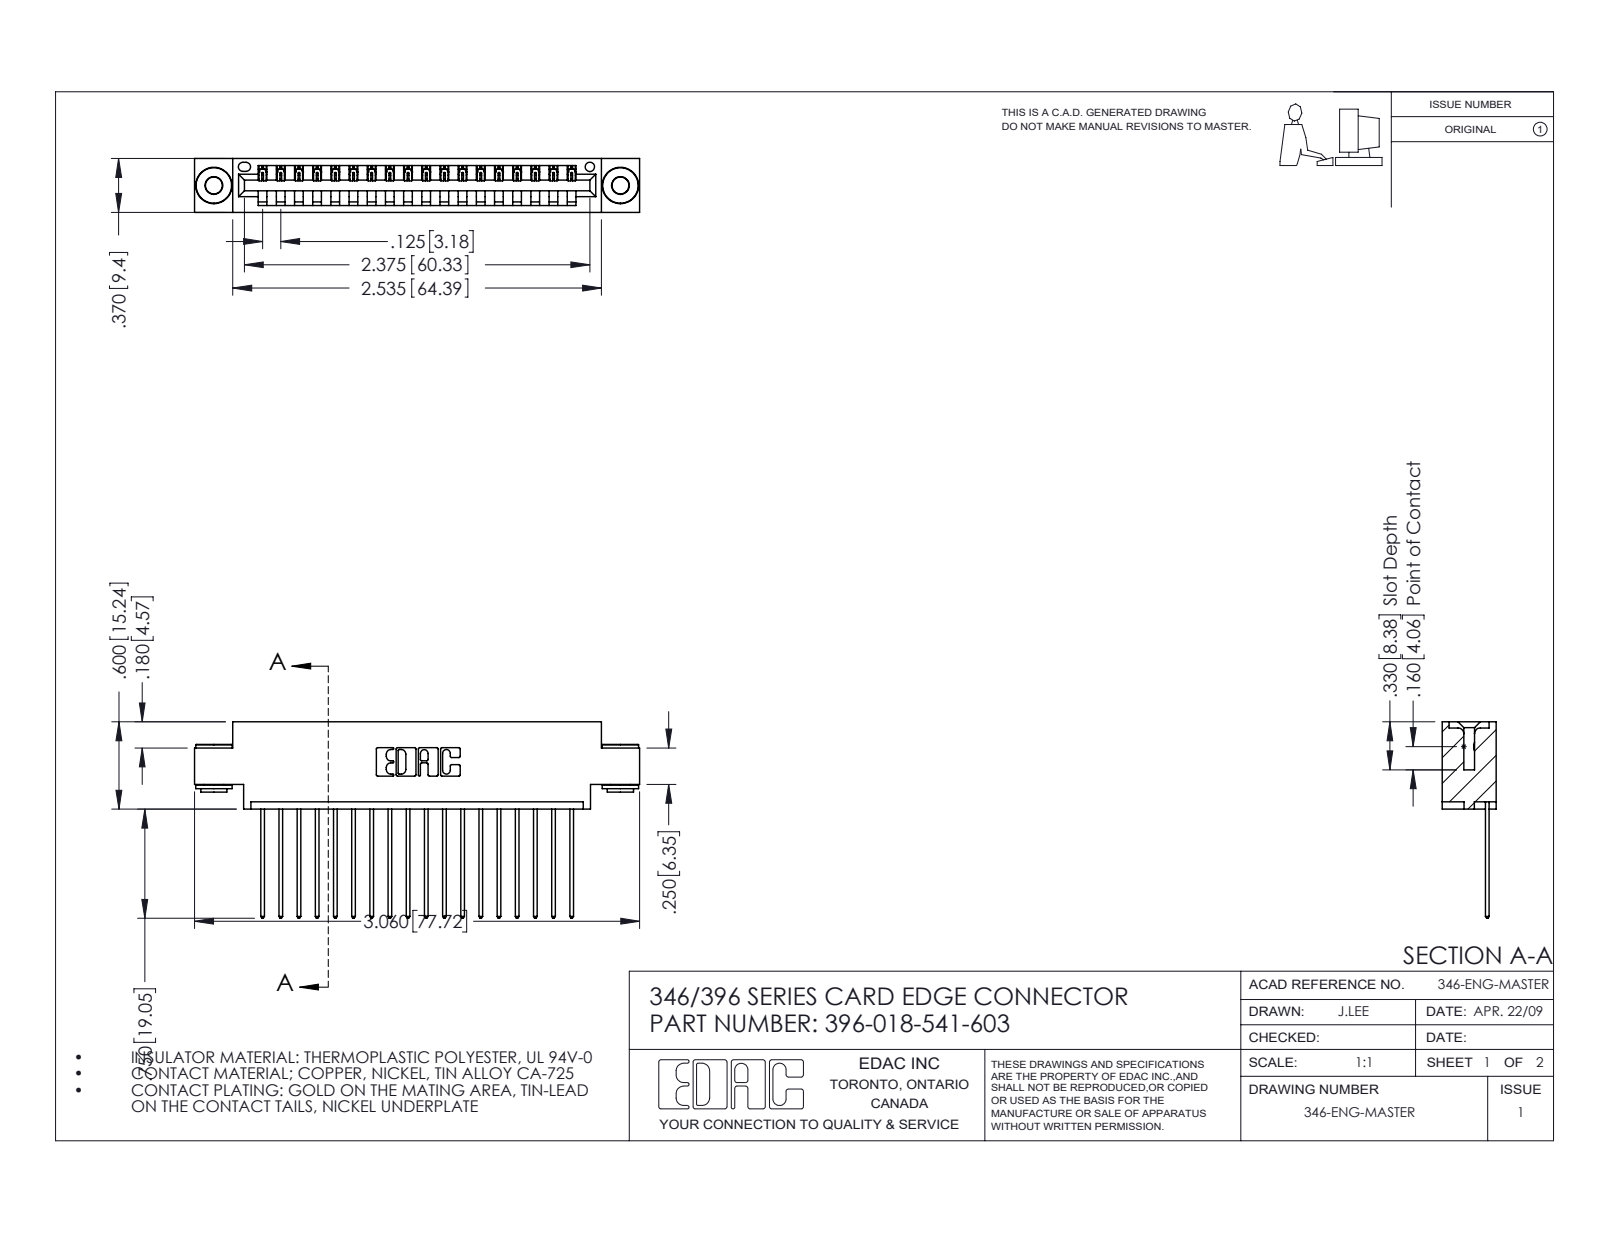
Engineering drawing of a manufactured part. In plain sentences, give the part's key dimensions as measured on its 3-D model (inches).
The part is named "396-018-541-603; 345-250-002_345-250-002-102; 346 Part_0.170 Offset - 0.156 Dia-TH; 345-292-001_345-293-141". Its 3-D file was written by "SolidWorks 2016 (CONFIG_CONTROL_DESIGN)". It is 21 solids with 1208 faces: 810 planar, 390 cylindrical and 8 other. Overall it measures 3.06 by 1.35 by 0.37 inches. Its volume is 0.439 cubic inches and its surface area 14.68 square inches. Round holes: 2 of diameter 0.116, 2 of diameter 0.156, 1 of diameter 0.064. Round bosses or shafts: 2 of diameter 0.25, 2 of diameter 0.18, 2 of diameter 0.136. Partial cylindrical surfaces (rounded edges, fillets, slot ends): 36 of radius 0.006, 36 of radius 0.01, 22 of radius 0.01, 6 of radius 0.007, 6 of radius 0.031, 3 of radius 0.026, 2 of radius 0.031, 2 of radius 0.04. The main face-to-face distances are 0.048, 0.322, 0.37, 0.25, 0.025, 0.072, 0.298, 0.148, 0.222, 0.1. The hole center spacings are 0.246, 2.588, 2.795.
